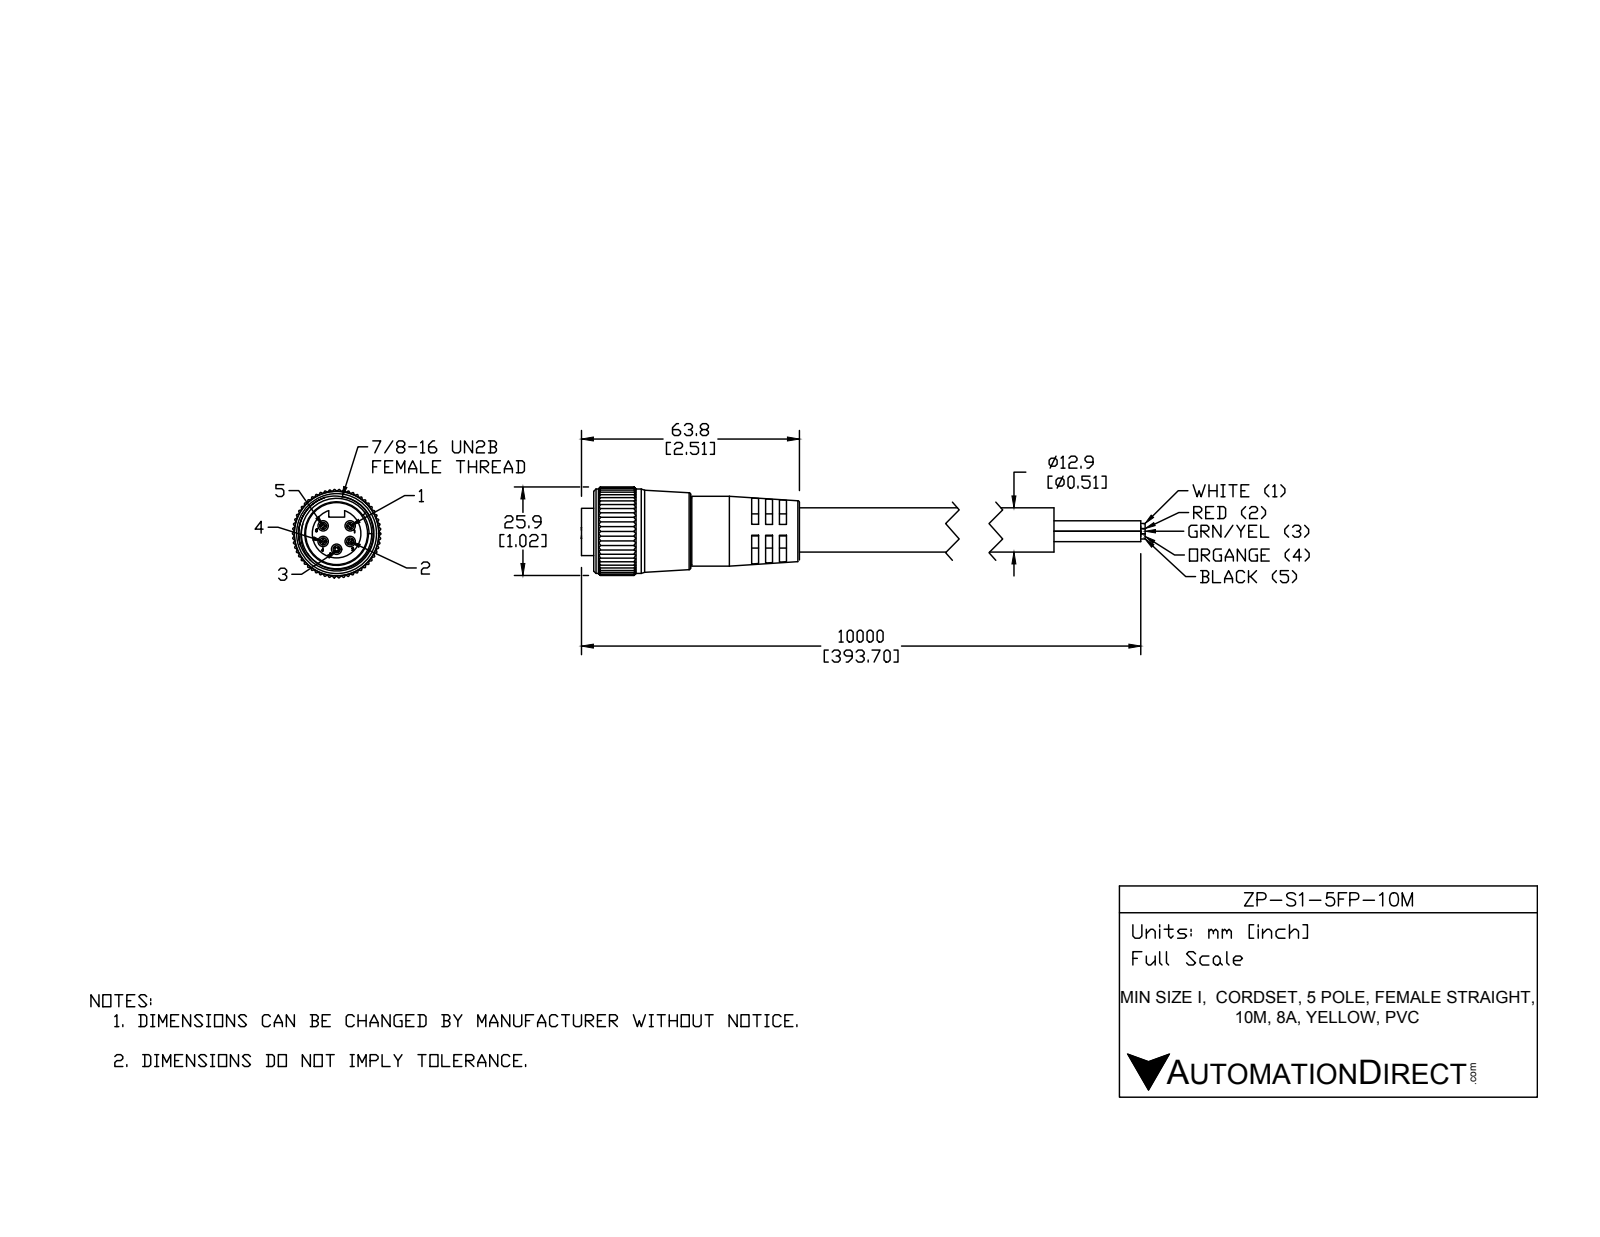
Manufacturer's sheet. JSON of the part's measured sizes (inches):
{"part_name": "ZP-S1-5FP-10M", "step_written_by": "SolidWorks 2015 (AUTOMOTIVE_DESIGN)", "units": "inches", "bodies": {"solids": 2, "faces": 576, "planar": 216, "cylindrical": 310, "other": 50}, "overall_size": [4.339, 2.083, 1.017], "volume_in3": 1.867, "surface_area_in2": 19.41, "round_holes": [[0.12, 5], [0.714, 1], [0.81, 1], [0.827, 1]], "round_bosses_or_shafts": [[0.509, 2], [0.972, 1], [0.803, 1], [0.768, 1], [0.56, 1]], "partial_cylinders_radius": [[0.01, 165], [0.207, 1], [0.509, 1]], "face_to_face_distances": [0.159, 0.079, 0.08, 0.237, 0.317, 0.239, 0.832, 0.911, 0.991, 1.069], "hole_center_spacings": [0.18, 0.312, 0.18, 0.36]}
